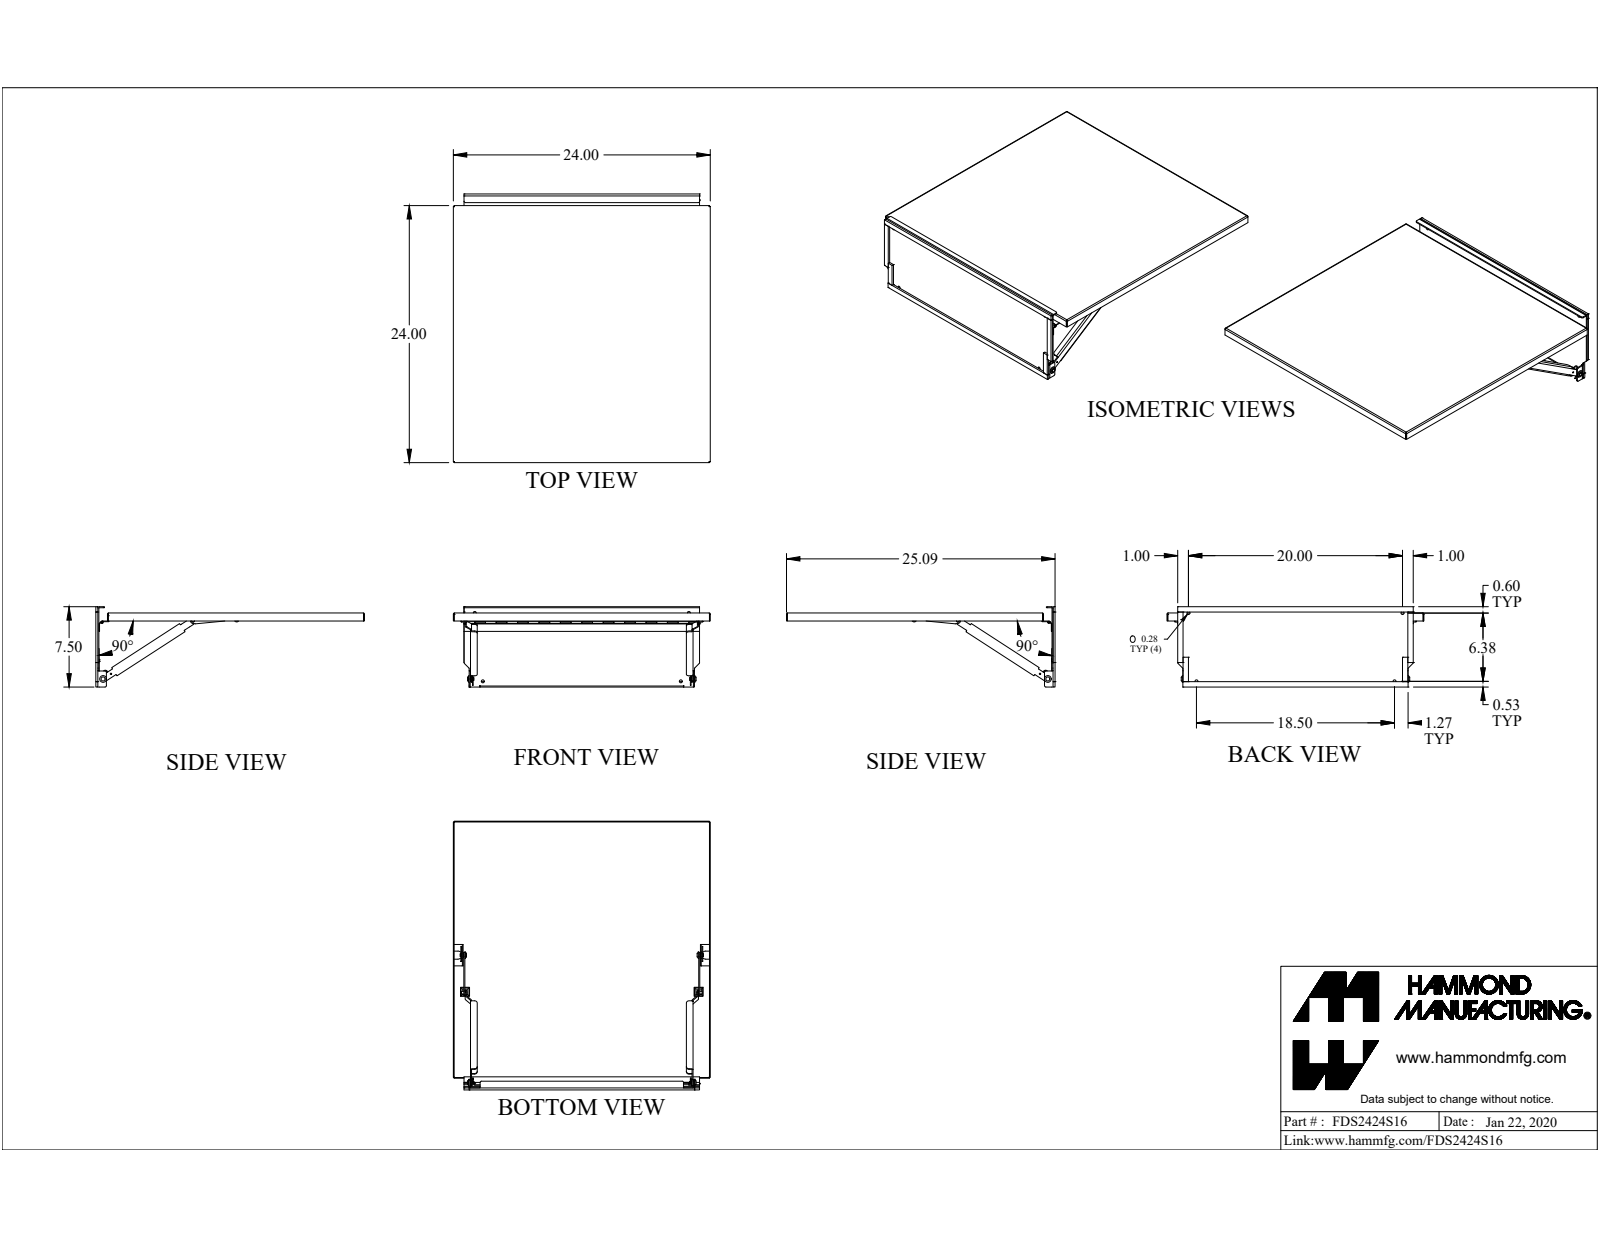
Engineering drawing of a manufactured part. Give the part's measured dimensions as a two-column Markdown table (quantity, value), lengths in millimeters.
| quantity | value |
| --- | --- |
| part name | FDS2424S16 |
| STEP written by | SolidWorks 2019 (CONFIG_CONTROL_DESIGN) |
| units | millimeters |
| bodies | 42 solids, 660 faces (399 planar, 212 cylindrical, 49 other) |
| overall size | 637.3 × 609.6 × 190.5 |
| volume | 1 261 000 mm³ |
| surface area | 1 281 000 mm² |
| round holes (diameter × count) | 2.4 × 4, 7.1 × 4, 6.7 × 3, 3.2 × 2, 6.5 × 2, 6.6 × 2, 7.2 × 2, 2.8 × 1, 3.2 × 1, 6.7 × 1 |
| round bosses / shafts (diameter × count) | 6.4 × 3, 15.9 × 2, 13 × 2, 9.5 × 2, 15.9 × 1, 12.7 × 1, 5.9 × 1, 2.5 × 1 |
| partial cylindrical surfaces (radius × count) | 6.4 × 16, 1.2 × 12, 3.6 × 12, 3.2 × 11, 0.9 × 6, 2.7 × 6, 9.5 × 6, 1.3 × 4 |
| main face-to-face distances | 1.8, 2.4, 607.8, 22.3, 1.6, 609.6, 7.2, 4.7, 24.7, 29.5 |
| hole center spacings | 33.6, 160.8, 163, 216.3, 515.1, 540.3, 543, 577.3 |
